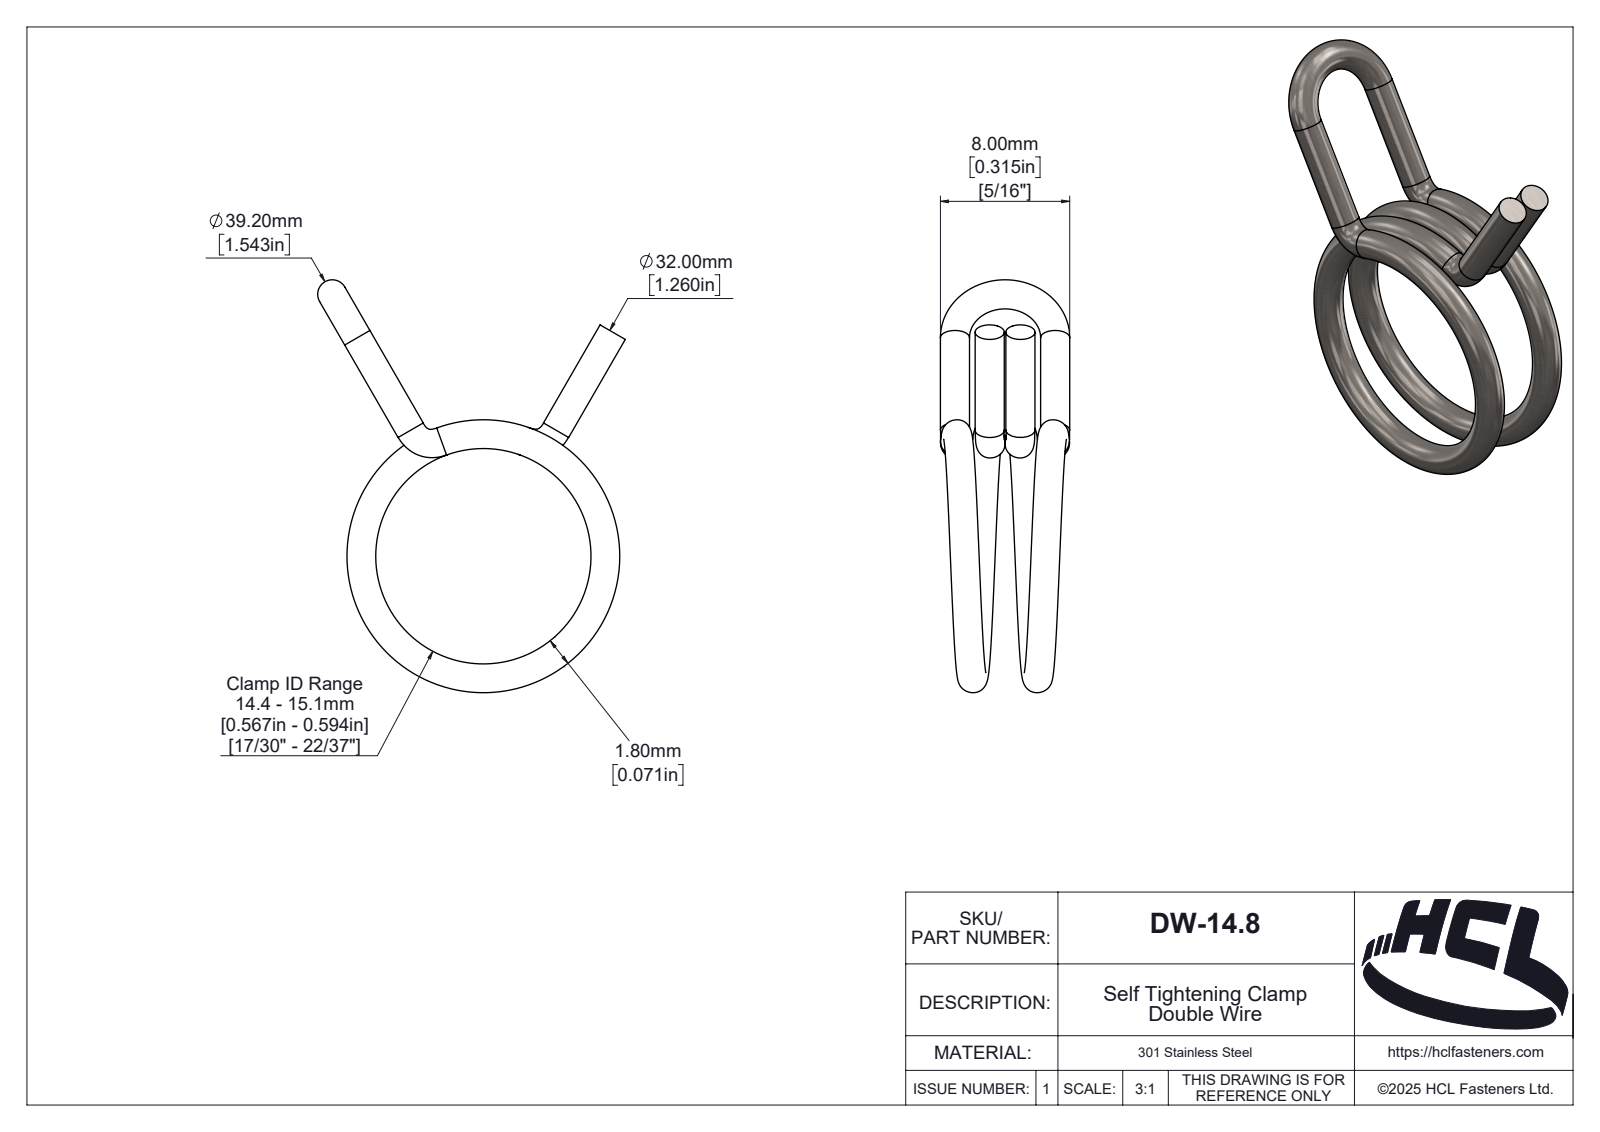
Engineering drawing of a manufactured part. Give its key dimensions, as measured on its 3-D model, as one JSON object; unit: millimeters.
{"part_name": "DW-14.8", "step_written_by": "SolidWorks 2025 (AUTOMOTIVE_DESIGN)", "units": "millimeters", "bodies": {"solids": 1, "faces": 132, "planar": 14, "cylindrical": 53, "other": 65}, "overall_size": [25.53, 19.03, 8], "volume_mm3": 380, "surface_area_mm2": 856, "round_bosses_or_shafts": [[1.8, 4]], "partial_cylinders_radius": [[0.16, 1], [0.2, 1], [0.21, 1], [0.26, 1], [0.36, 1], [0.48, 1], [0.6, 1], [0.68, 1]]}
